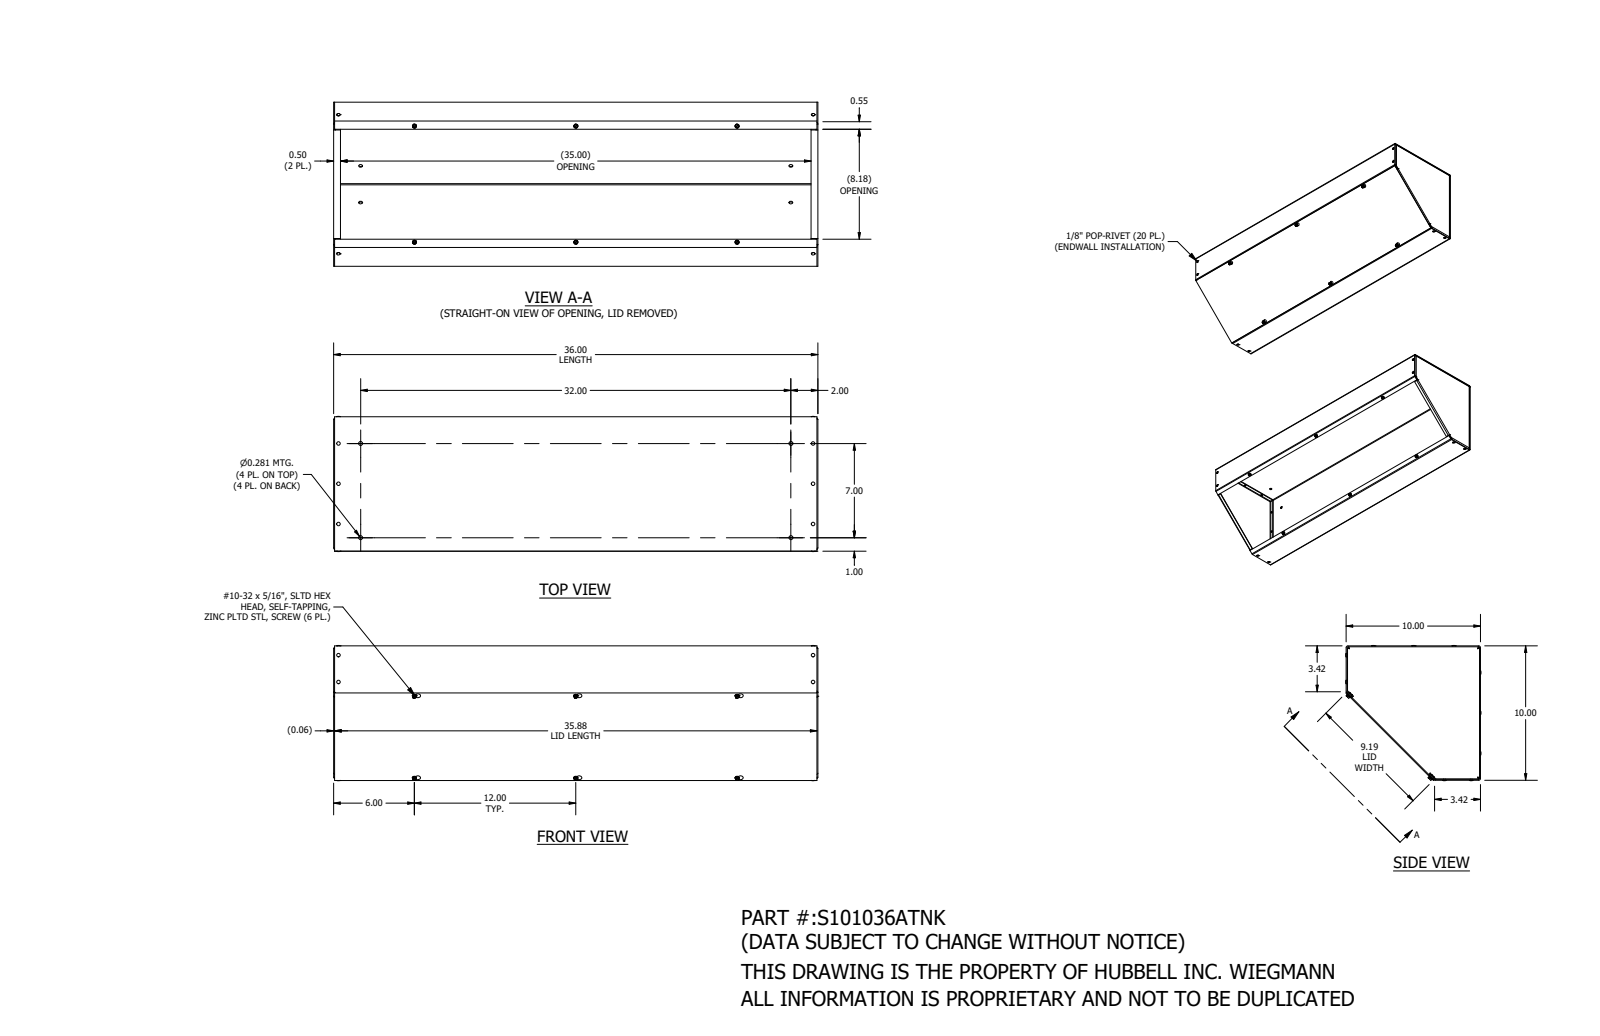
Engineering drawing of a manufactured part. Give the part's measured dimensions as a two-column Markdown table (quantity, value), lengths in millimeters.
| quantity | value |
| --- | --- |
| part name | S101036ATNK |
| STEP written by | SolidWorks 2021 (AUTOMOTIVE_DESIGN) |
| units | millimeters |
| bodies | 30 solids, 1430 faces (342 planar, 412 cylindrical, 676 other) |
| overall size | 914.4 × 256 × 256 |
| volume | 1 814 000 mm³ |
| surface area | 1 948 000 mm² |
| round holes (diameter × count) | 3.3 × 20, 7.1 × 8, 4.3 × 6, 10.3 × 6 |
| round bosses / shafts (diameter × count) | 6.7 × 20, 3.2 × 19, 8 × 6, 4.6 × 6, 3.2 × 1 |
| partial cylindrical surfaces (radius × count) | 1.6 × 40, 3.5 × 15, 1.6 × 13, 2.8 × 6, 1.6 × 2 |
| main face-to-face distances | 1.9, 252.1, 250.2, 254, 912.5, 1.7, 914.4, 910.6, 3.6, 3.8 |
| hole center spacings | 897, 76.2, 304.8, 900.2, 6.4, 18, 32.8, 42.1 |
